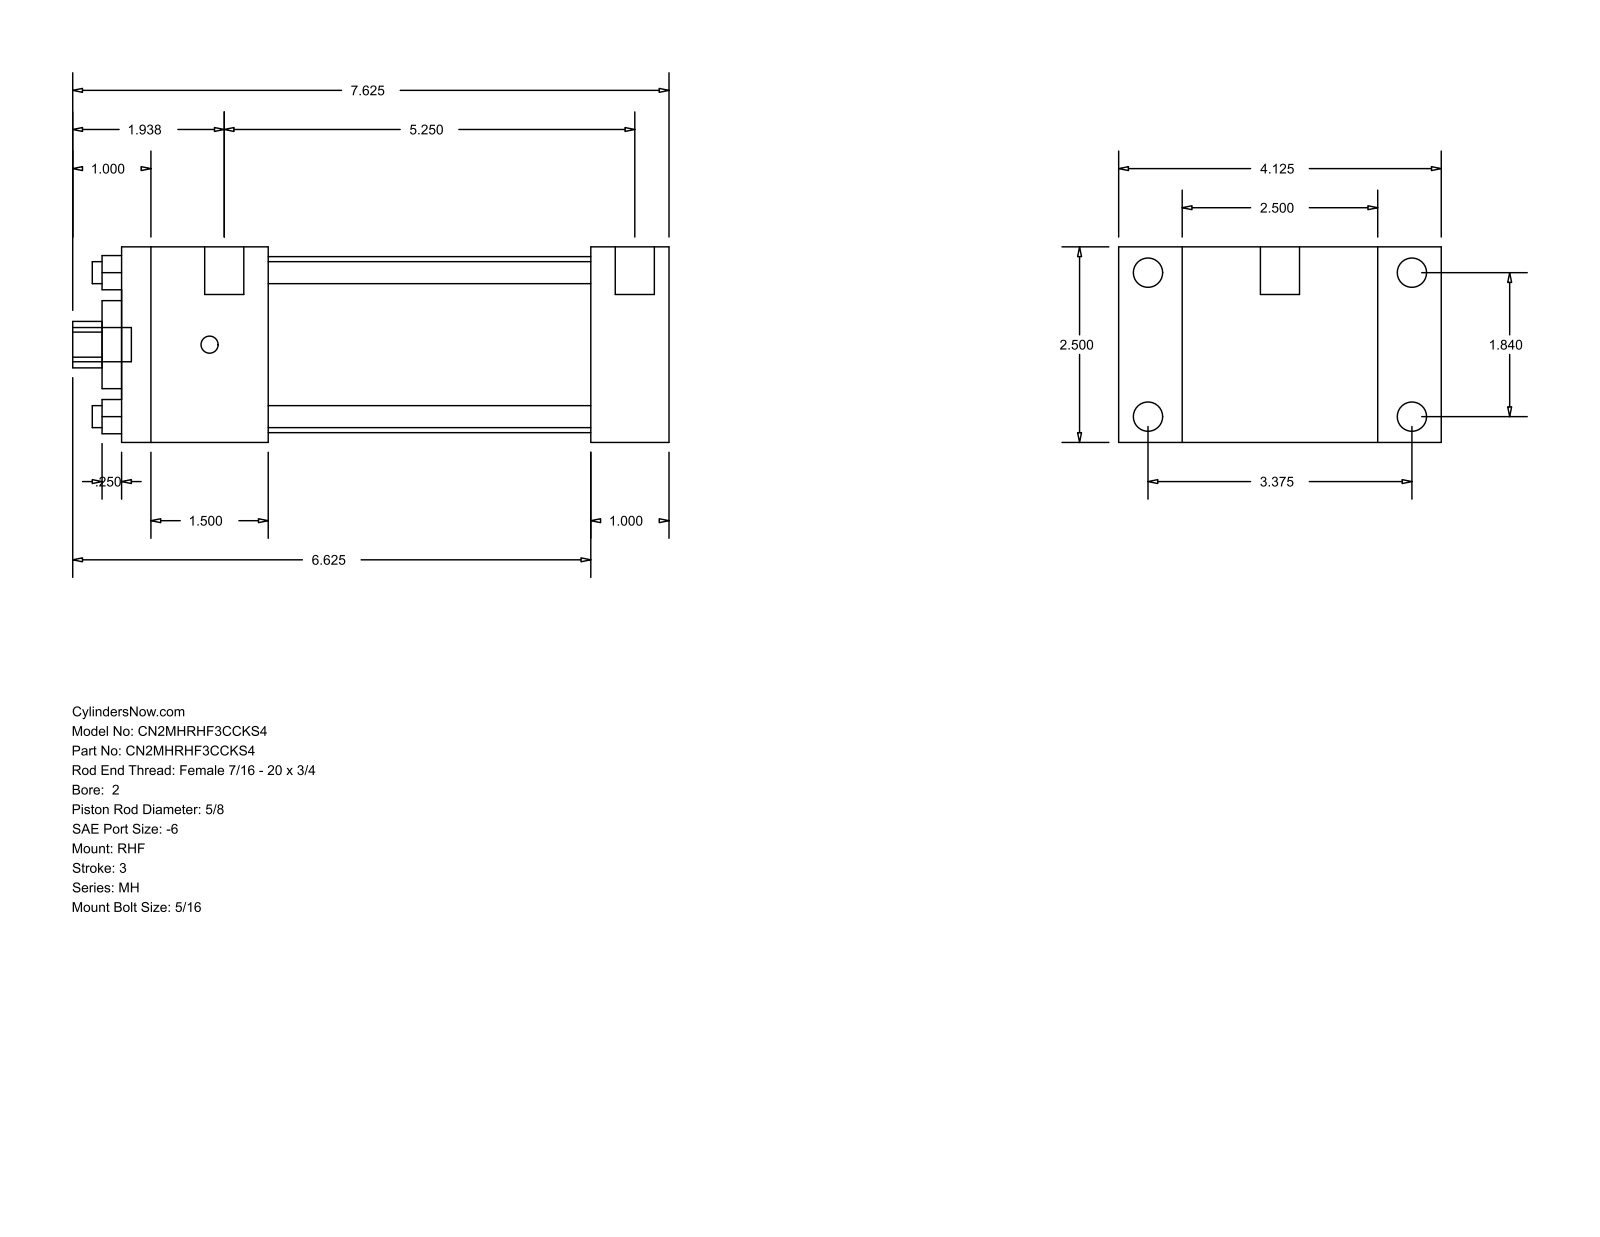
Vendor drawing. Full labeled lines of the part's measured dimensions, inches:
Part name (STEP PRODUCT): MH_RHF__0200_0.625
STEP written by: GSSL Pune (CONFIG_CONTROL_DESIGN)
Units: inches
Bodies: 0 solids, 88 faces (60 planar, 28 cylindrical, 0 other)
Overall size (bounding box): 7.625 × 4.125 × 2.5
Round holes (diameter × count): ⌀0.281 ×4, ⌀0.625 ×1, ⌀1.125 ×1, ⌀2.25 ×1
Round bosses / shafts (diameter × count): ⌀0.375 ×4, ⌀0.219 ×4, ⌀0.5 ×2, ⌀0.437 ×1
Partial cylindrical surfaces — rounded edges, fillets, slot ends (radius × count): R0.297 ×1
Main face-to-face distances: 2.5, 1, 0.813, 3.313, 6, 7, 4.125, 1.875, 5.125, 0.25
Hole centre spacings: 1.301, 1.84, 2.602
